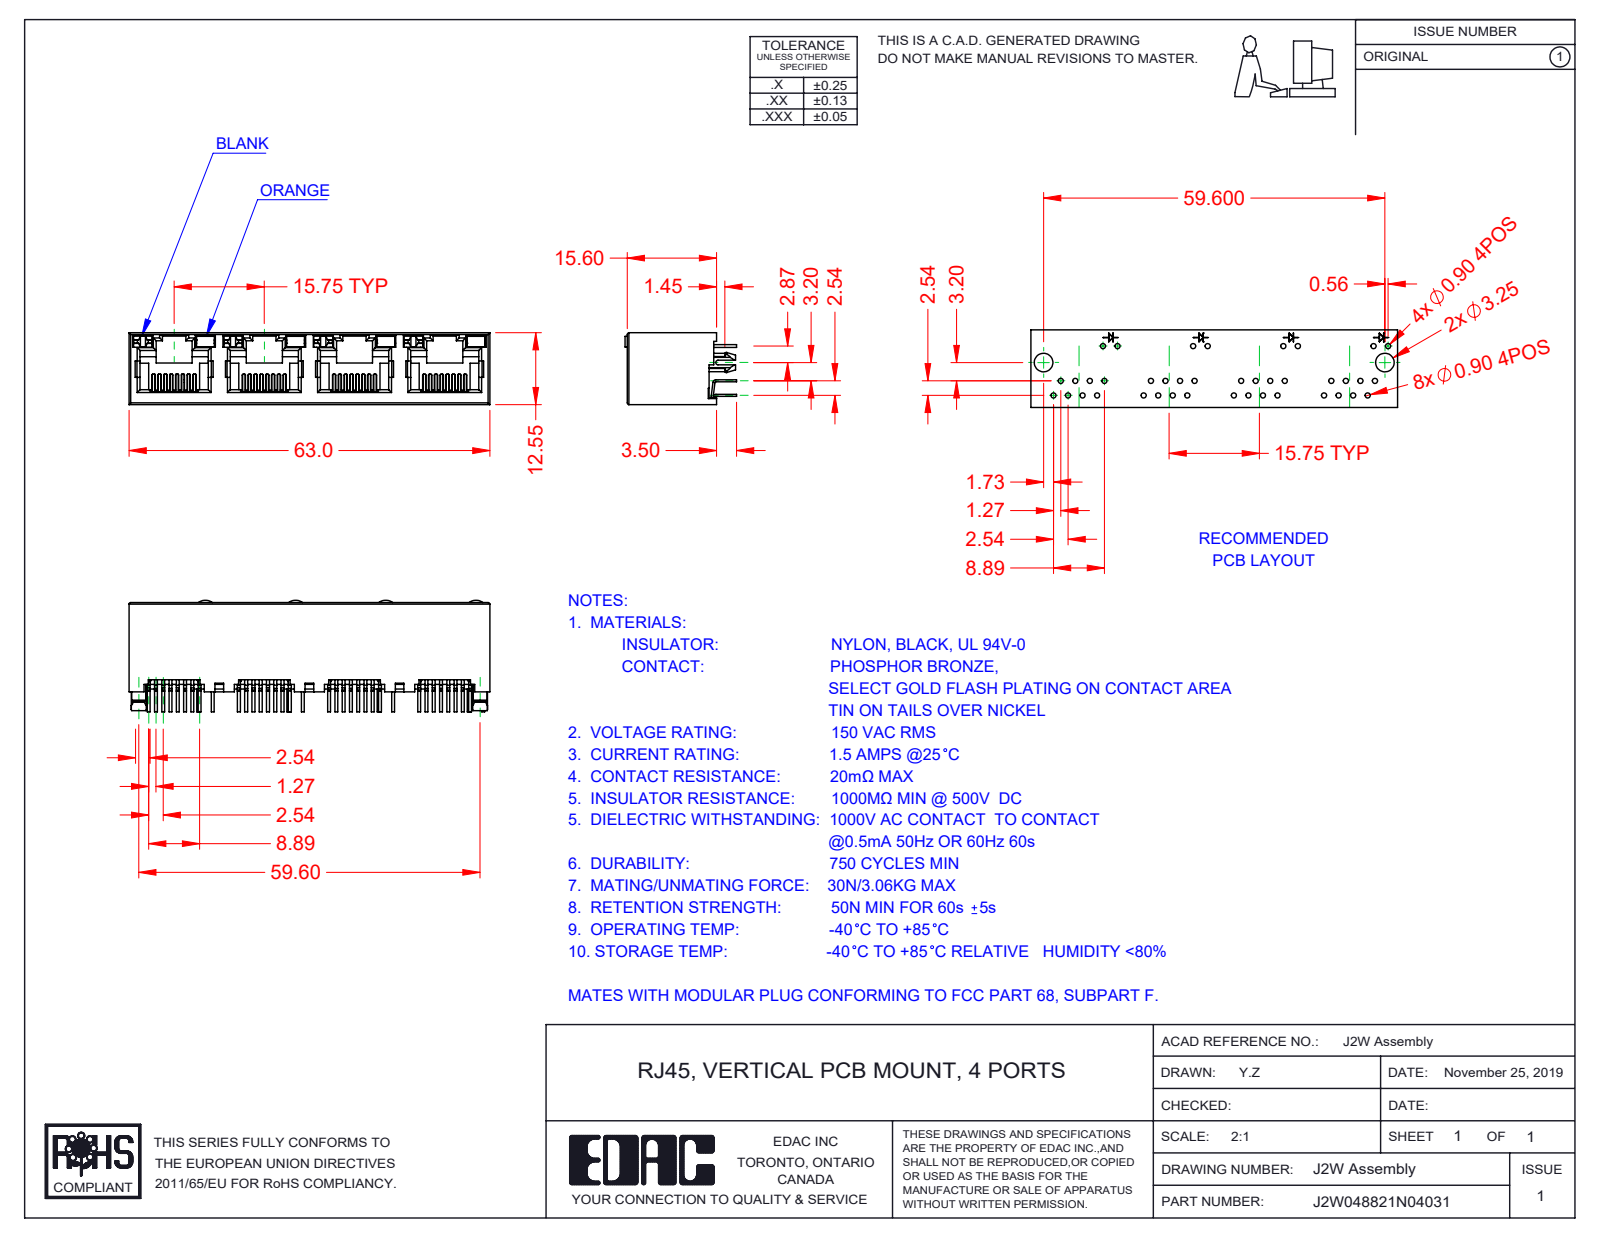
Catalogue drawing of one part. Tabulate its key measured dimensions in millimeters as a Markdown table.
| quantity | value |
| --- | --- |
| part name | 2W Insulator; 2W LED RH_4-Orange; 2W LED LH_0-Blank; 2W Contacts (+2 more) |
| STEP written by | SolidWorks 2020 (CONFIG_CONTROL_DESIGN) |
| units | millimeters |
| bodies | 41 solids, 3007 faces (2508 planar, 441 cylindrical, 58 other) |
| overall size | 63 × 19.5 × 12.55 |
| volume | 5 212 mm³ |
| surface area | 12 695 mm² |
| partial cylindrical surfaces (radius × count) | 0.15 × 64, 0.2 × 29, 0.5 × 28, 0.3 × 14, 0.45 × 8, 2 × 4, 0.25 × 2, 1.5 × 2 |
| main face-to-face distances | 12.55, 11.9, 0.65, 15.75, 0.36, 1.5, 0.78, 0.6, 11.3, 31.5 |
